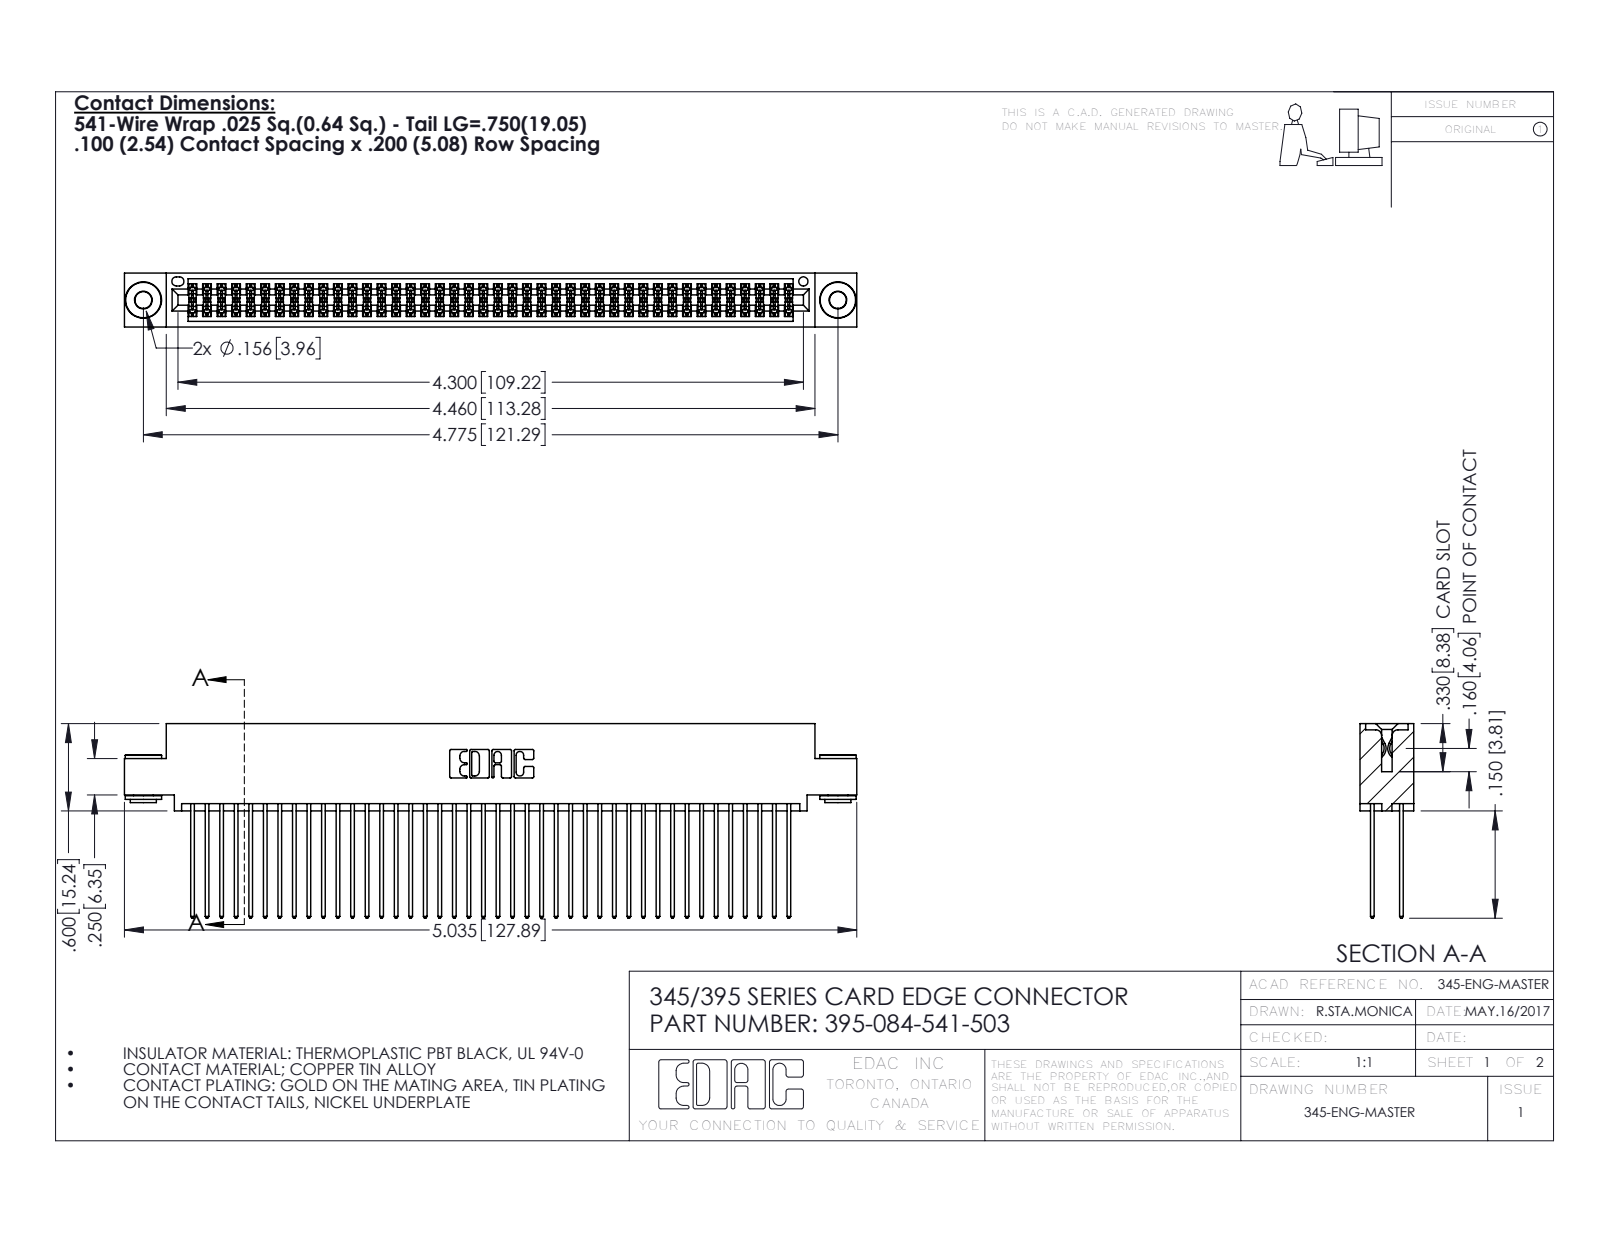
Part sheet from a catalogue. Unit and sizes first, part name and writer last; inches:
Units: inches
Overall size (bounding box): 5.035 × 1.337 × 0.37
Round holes (diameter × count): ⌀0.116 ×2, ⌀0.156 ×2, ⌀0.064 ×1
Round bosses / shafts (diameter × count): ⌀0.25 ×2, ⌀0.18 ×2, ⌀0.136 ×2
Partial cylindrical surfaces — rounded edges, fillets, slot ends (radius × count): R0.006 ×126, R0.01 ×84, R0.01 ×22, R0.007 ×6, R0.031 ×6, R0.026 ×3, R0.014 ×2, R0.019 ×2
Main face-to-face distances: 0.072, 0.298, 0.2, 0.025, 0.098, 0.272, 0.225, 0.37, 0.175, 0.149
Hole centre spacings: 0.27, 4.539, 4.775
Volume: 0.784 in³ · Surface area: 33.42 in²
Bodies: 87 solids, 4368 faces (2866 planar, 1494 cylindrical, 8 other)
Part name (STEP PRODUCT): 345-292-001_345-293-141; 395-084-541-503; 345 Part_0.110 Offset - 0.156 Dia-TH; 345-250-002_345-250-002-102
STEP written by: SolidWorks 2016 (CONFIG_CONTROL_DESIGN)
